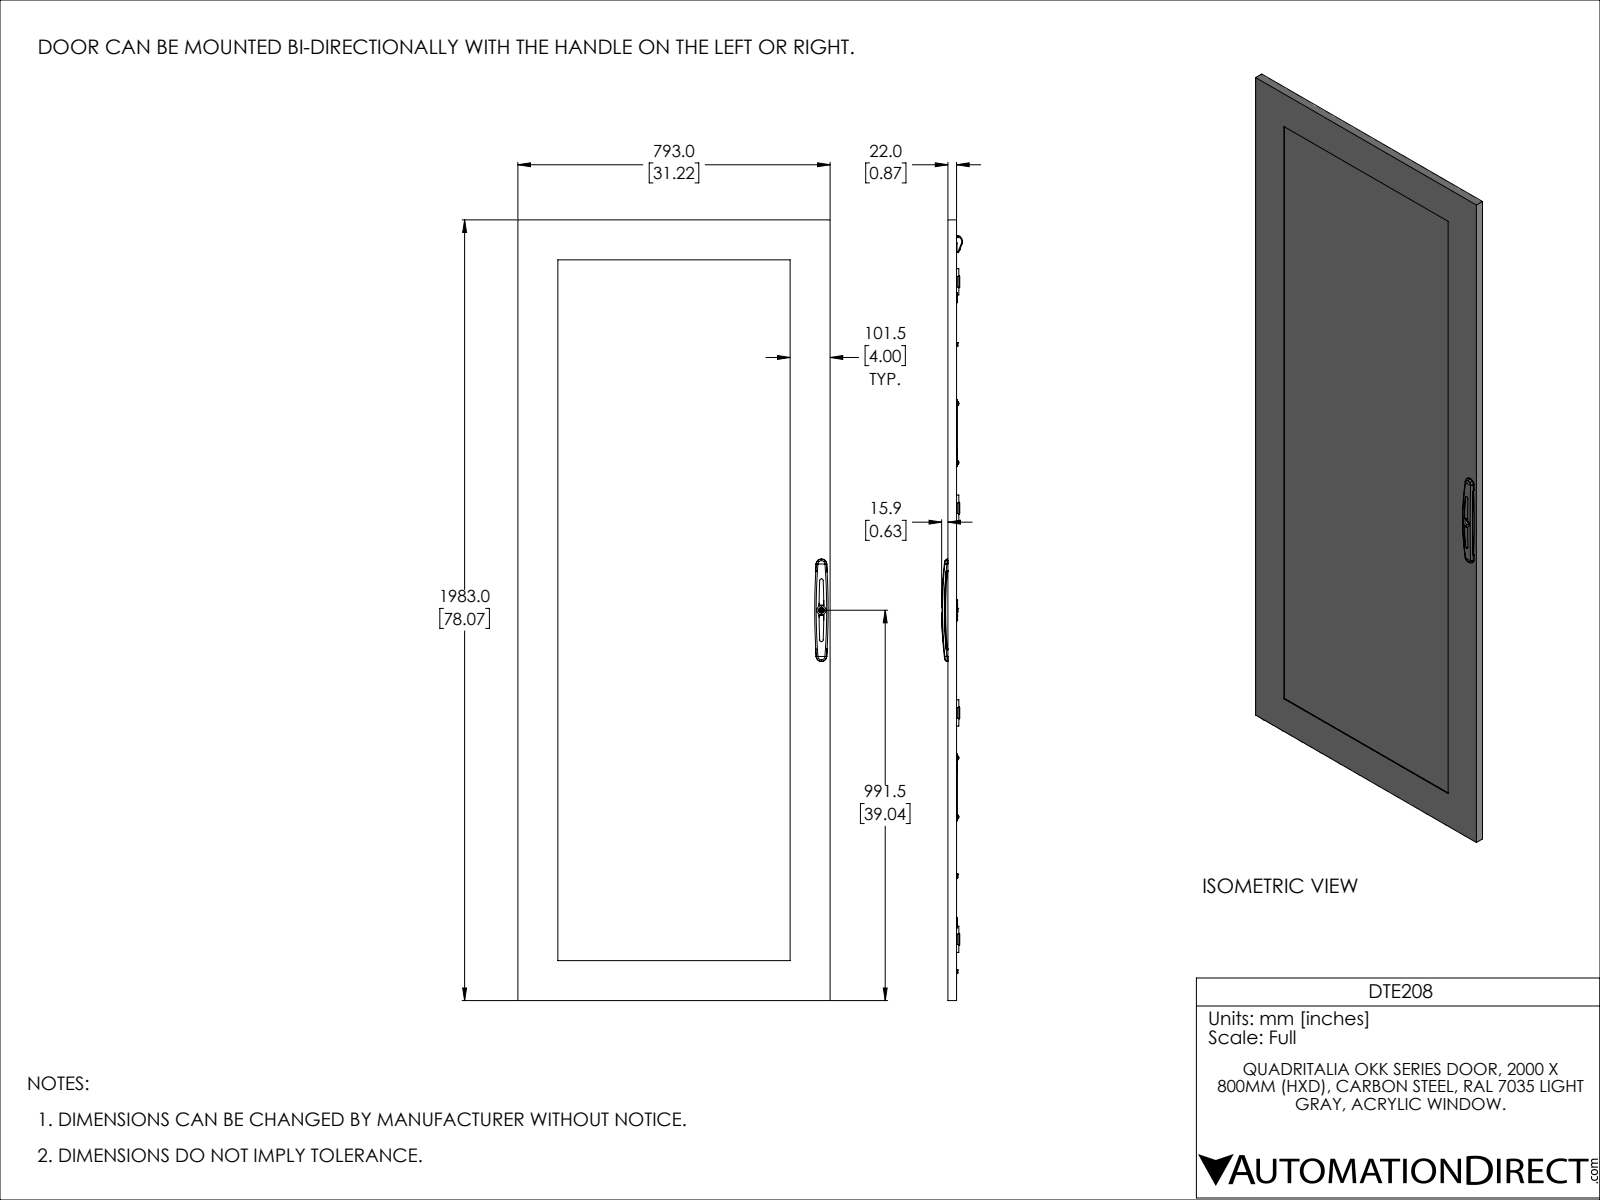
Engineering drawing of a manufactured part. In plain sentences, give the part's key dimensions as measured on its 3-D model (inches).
The part is named "DTE208". Its 3-D file was written by "SolidWorks 2021 (CONFIG_CONTROL_DESIGN)". It is 96 solids with 3419 faces: 1651 planar, 1207 cylindrical and 561 other. Overall it measures 78.071 by 31.22 by 2.091 inches. Its volume is 440 cubic inches and its surface area 7 497 square inches. Round holes: 144 of diameter 0.167, 29 of diameter 0.315, 18 of diameter 0.354, 10 of diameter 0.194, 8 of diameter 0.01, 8 of diameter 0.197, 4 of diameter 0.244, 4 of diameter 0.276, 3 of diameter 0.205, 2 of diameter 0.134, 2 of diameter 0.169, 2 of diameter 0.173. Round bosses or shafts: 21 of diameter 0.276, 17 of diameter 0.236, 10 of diameter 0.394, 10 of diameter 0.283, 9 of diameter 0.197, 8 of diameter 0.193, 2 of diameter 0.315, 2 of diameter 0.157. Partial cylindrical surfaces (rounded edges, fillets, slot ends): 74 of radius 0.012, 70 of radius 0.039, 36 of radius 0.059, 33 of radius 0.02, 28 of radius 0.098, 16 of radius 0.177, 15 of radius 0.079, 10 of radius 0.227. The main face-to-face distances are 0.157, 0.079, 0.236, 0.059, 0.728, 0.787, 0.669, 25.984, 0.866, 0.63. The hole center spacings are 0.984, 1.969, 2.953, 8.858, 3.937, 4.921, 5.906, 6.89.
